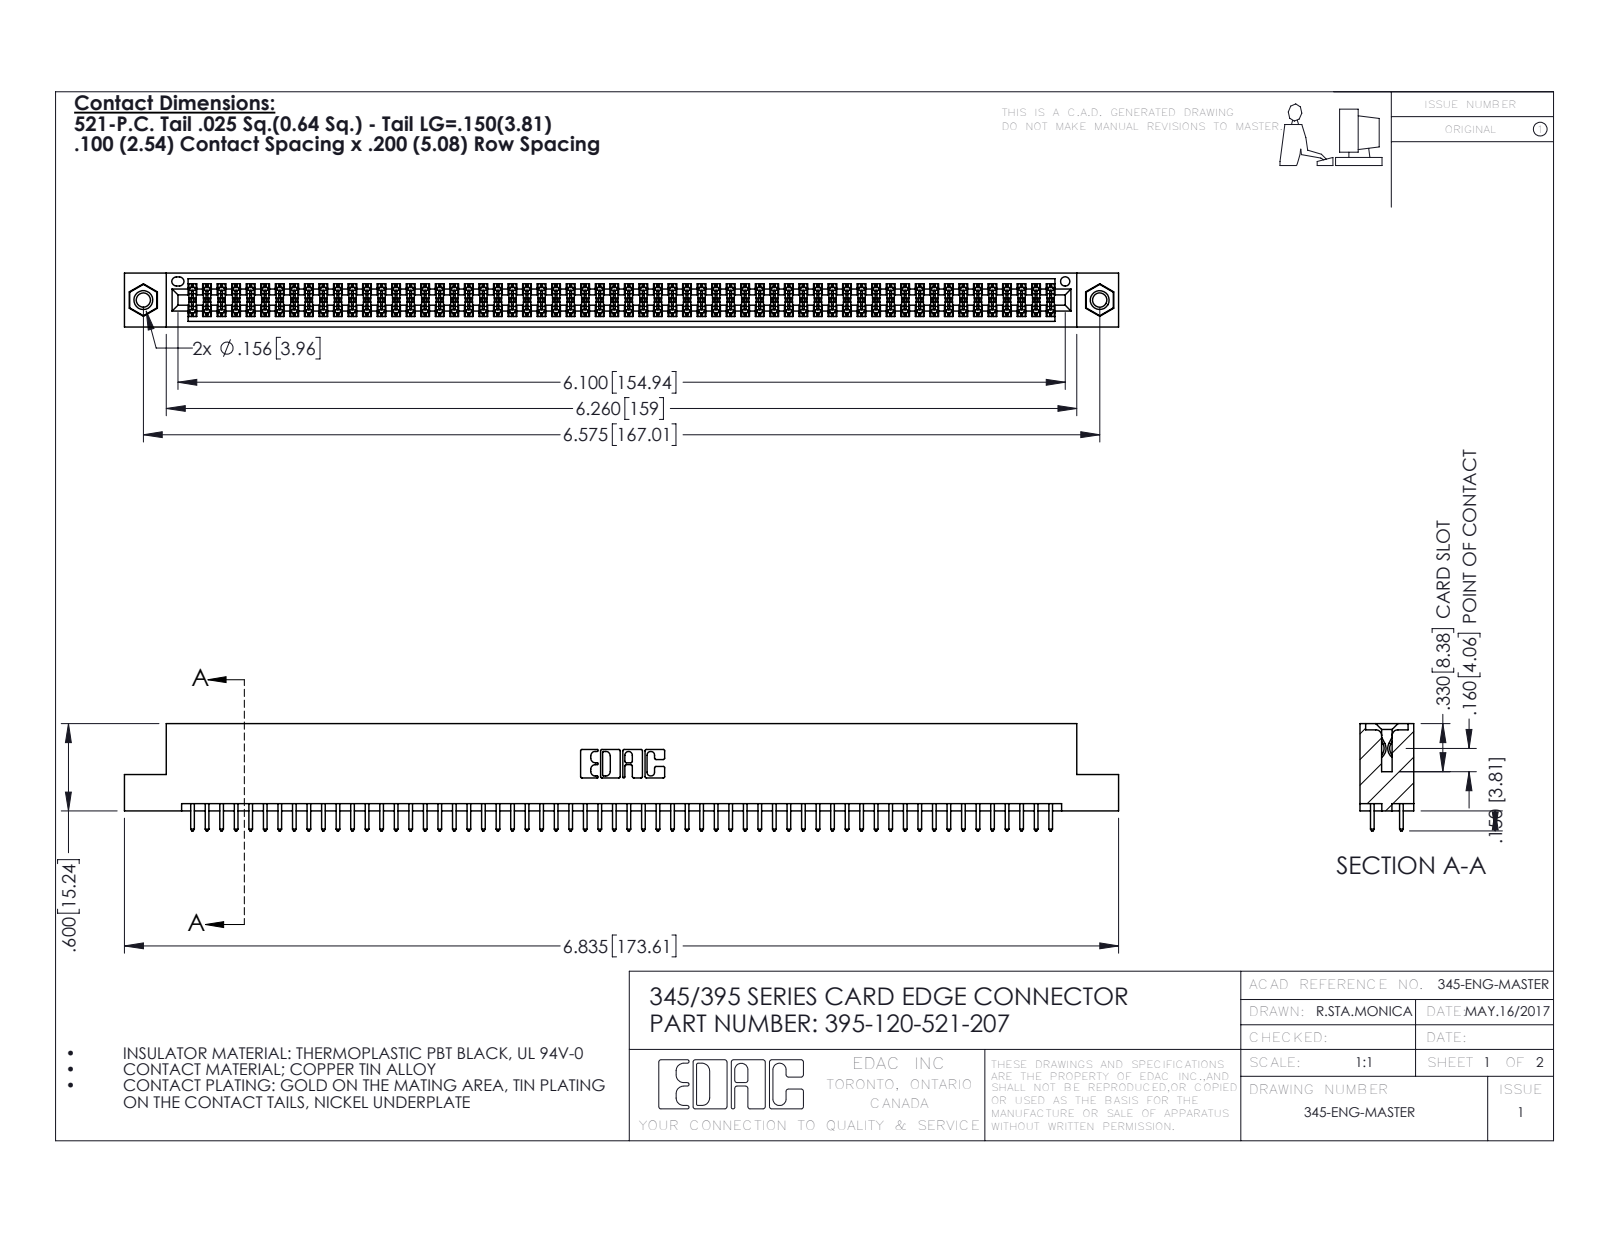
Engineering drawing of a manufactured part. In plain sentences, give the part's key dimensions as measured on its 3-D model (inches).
The part is named "345-292-001_345-293-121; 345-250-001_345-250-005-103; 395-120-521-207; 345 Part_Flush Mounting Lugs - 0.156 Dia-TI". Its 3-D file was written by "SolidWorks 2016 (CONFIG_CONTROL_DESIGN)". It is 123 solids with 6186 faces: 4072 planar, 2098 cylindrical and 16 other. Overall it measures 6.835 by 0.737 by 0.37 inches. Its volume is 1.036 cubic inches and its surface area 38.97 square inches. Round holes: 2 of diameter 0.098, 2 of diameter 0.125, 2 of diameter 0.156, 1 of diameter 0.064. Round bosses or shafts: 2 of diameter 0.155. Partial cylindrical surfaces (rounded edges, fillets, slot ends): 180 of radius 0.006, 120 of radius 0.01, 22 of radius 0.01, 6 of radius 0.007, 6 of radius 0.031, 3 of radius 0.026, 2 of radius 0.014, 2 of radius 0.019. The main face-to-face distances are 0.072, 0.298, 0.2, 0.098, 0.272, 0.025, 0.37, 0.225, 0.175, 0.149. The hole center spacings are 0.27, 6.339, 6.575.
